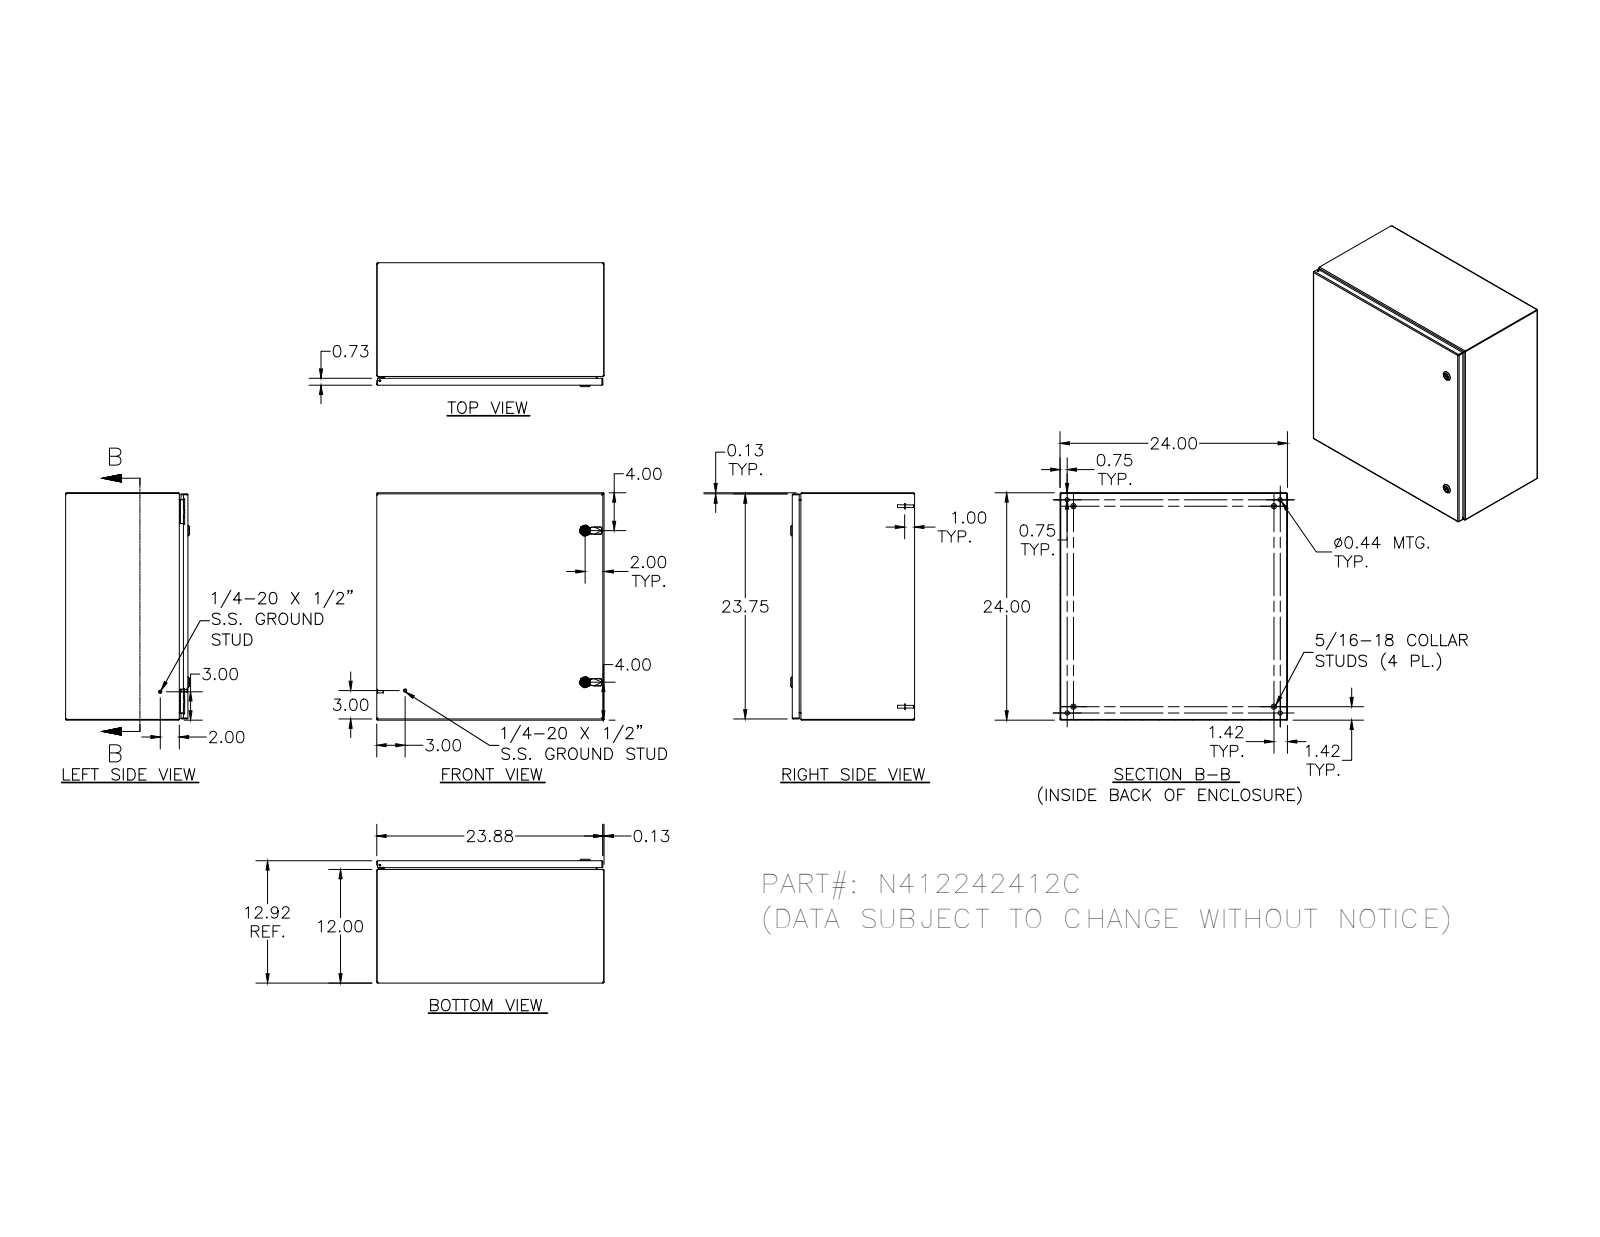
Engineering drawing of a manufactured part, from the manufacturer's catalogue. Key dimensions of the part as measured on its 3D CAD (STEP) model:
Part name (STEP PRODUCT): N412242412C
STEP written by: SolidWorks 2018 (AUTOMOTIVE_DESIGN)
Units: inches
Bodies: 40 solids, 1812 faces (704 planar, 676 cylindrical, 432 other)
Overall size (bounding box): 24 × 24 × 13.075
Volume: 185.2 in³ · Surface area: 5 025 in²
Round holes (diameter × count): ⌀0.188 ×5, ⌀0.093 ×4, ⌀0.152 ×4, ⌀0.167 ×4, ⌀0.172 ×4, ⌀0.437 ×4, ⌀0.156 ×2, ⌀0.197 ×2, ⌀0.315 ×2, ⌀0.394 ×2, ⌀0.402 ×2, ⌀0.634 ×2
Round bosses / shafts (diameter × count): ⌀0.25 ×10, ⌀0.563 ×4, ⌀0.36 ×4, ⌀0.32 ×4, ⌀0.3 ×4, ⌀0.256 ×4, ⌀0.164 ×4, ⌀0.131 ×4
Partial cylindrical surfaces — rounded edges, fillets, slot ends (radius × count): R0.012 ×54, R0.031 ×30, R0.05 ×26, R0.02 ×23, R0.105 ×20, R0.016 ×18, R0.125 ×16, R0.032 ×8
Main face-to-face distances: 0.074, 12.843, 0.074, 23.926, 23.852, 23.926, 24, 12.769, 12.917, 0.917
Hole centre spacings: 20, 0.66, 22.5, 0.656, 1.307, 1.965, 22.869, 0.5
